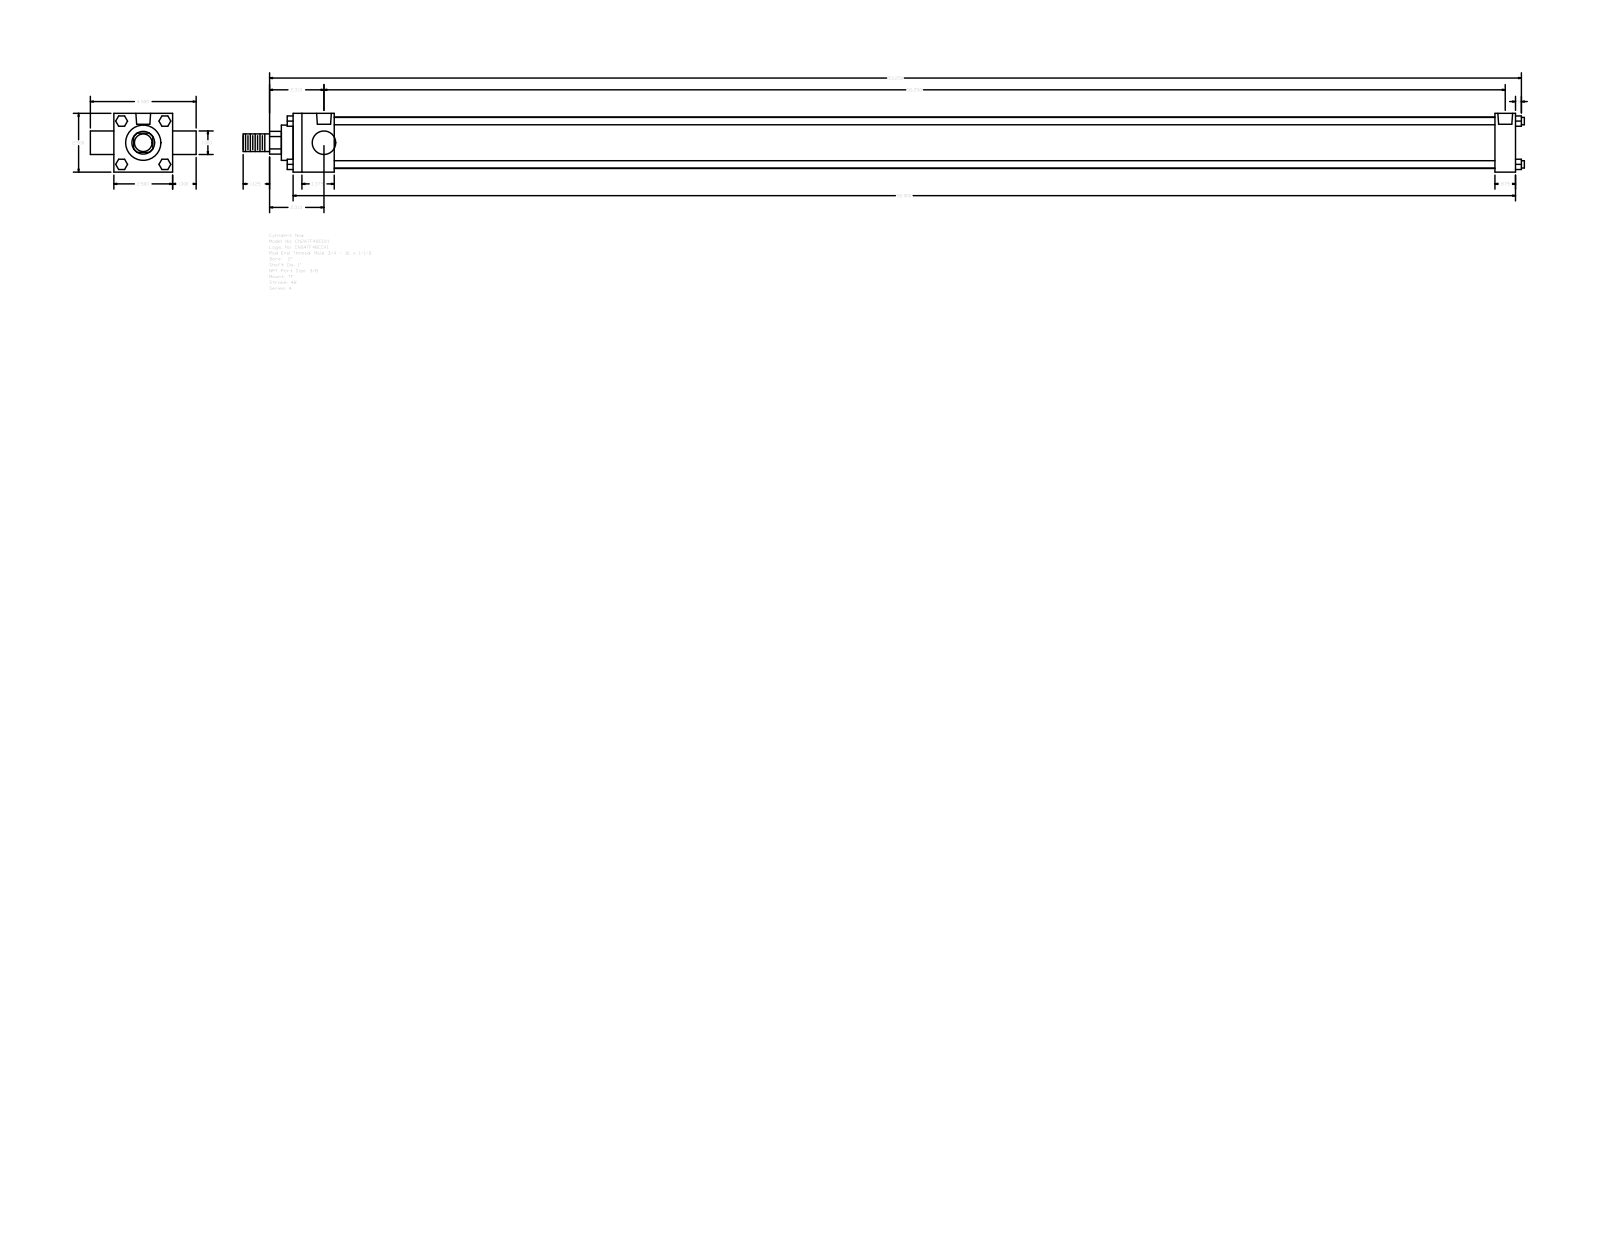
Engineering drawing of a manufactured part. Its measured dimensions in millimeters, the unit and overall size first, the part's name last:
Units: millimetres
Overall size (bounding box): 1384.3 × 114.3 × 63.5
Round holes (diameter × count): ⌀5.56 ×3, ⌀15.93 ×2
Round bosses / shafts (diameter × count): ⌀7.94 ×4, ⌀25.4 ×2, ⌀55.63 ×1, ⌀38.1 ×1, ⌀19.05 ×1
Partial cylindrical surfaces — rounded edges, fillets, slot ends (radius × count): R12.29 ×1
Main face-to-face distances: 63.5, 1320.8, 44.45, 1298.57, 1254.12, 1276.35, 22.23, 25.4, 88.9, 1333.5
Hole centre spacings: 1.59, 3.98, 1270.78, 1272.37, 1274.76, 1276.35
Bodies: 0 solids, 120 faces (92 planar, 28 cylindrical, 0 other)
Part name (STEP PRODUCT): A_TF__0200_1
STEP written by: GSSL Pune (CONFIG_CONTROL_DESIGN)
